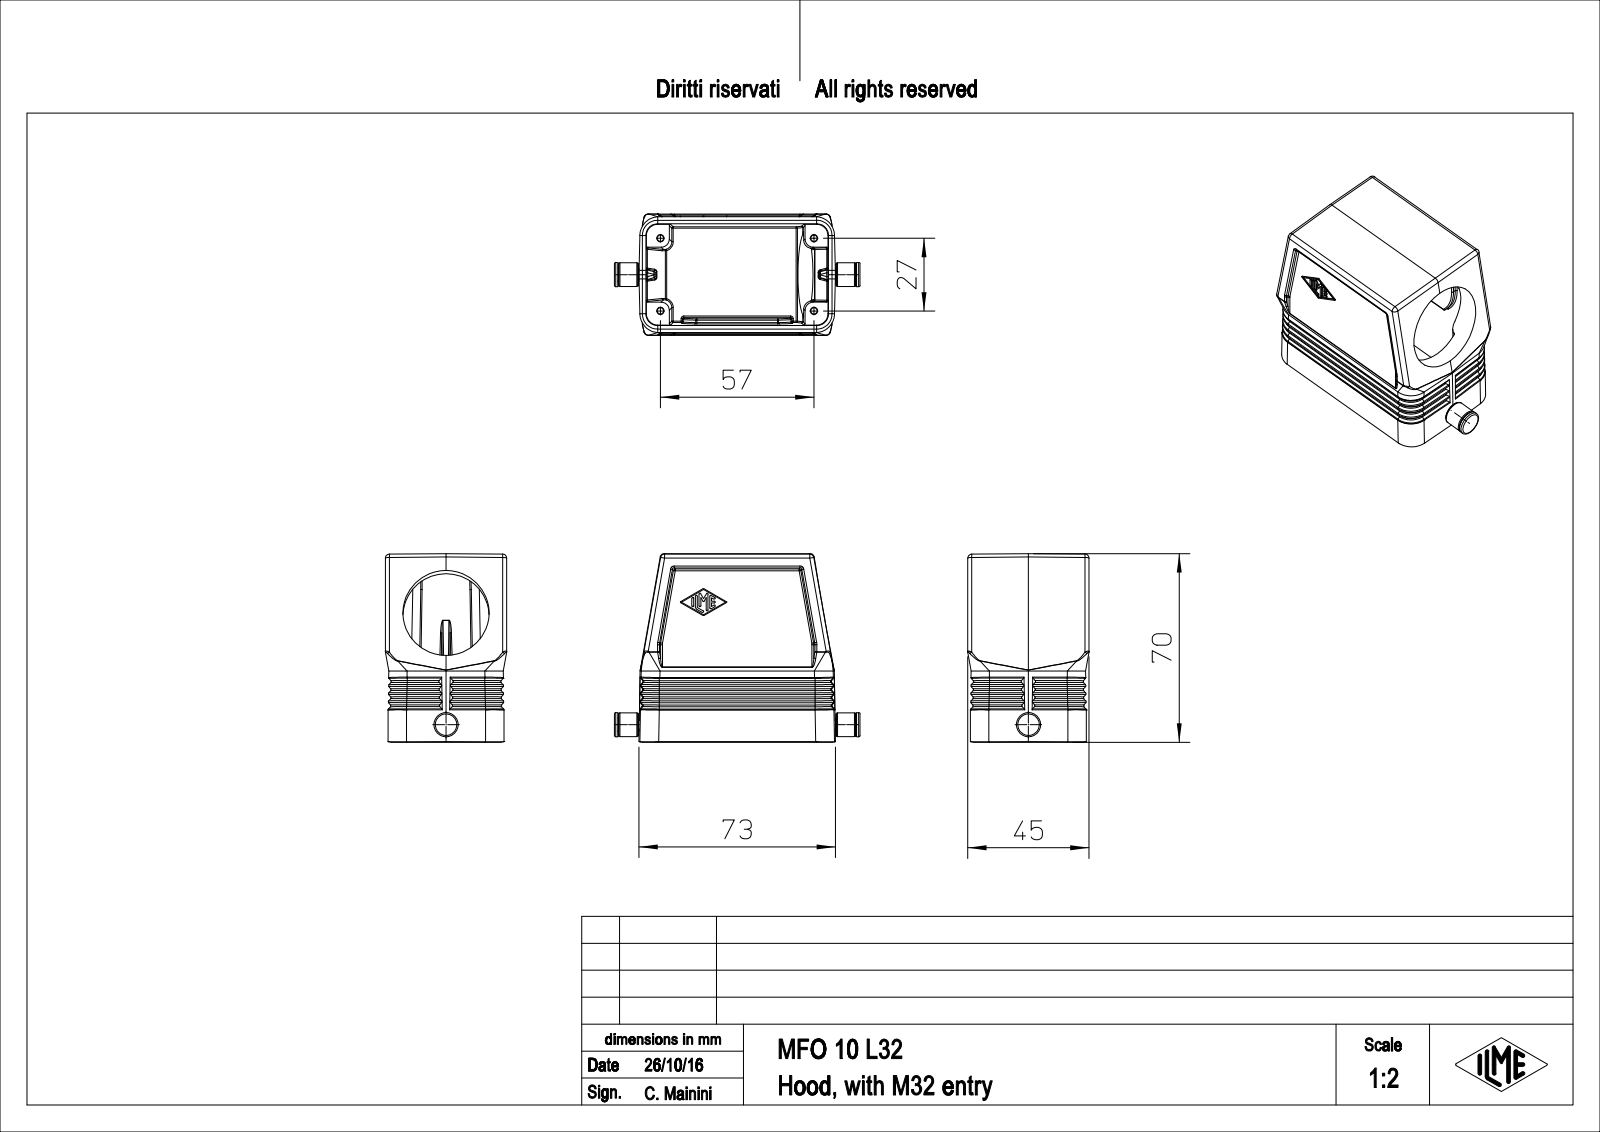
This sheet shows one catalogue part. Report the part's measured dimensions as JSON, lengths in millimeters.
{"part_name": "MFO_10_L32", "step_written_by": "PTC Creo Elements/Direct Modeling 19.0E 27-Jun-2016 (C) Parametric Technology GmbH (AUTOMOTIVE_DESIGN)", "units": "millimeters", "bodies": {"solids": 1, "faces": 431, "planar": 149, "cylindrical": 100, "other": 182}, "overall_size": [91.19, 70, 45], "volume_mm3": 65612, "surface_area_mm2": 33429, "round_holes": [[2.75, 4], [32, 1]], "round_bosses_or_shafts": [[9, 1], [8.8, 1], [4.8, 1], [3.2, 1]], "partial_cylinders_radius": [[0.5, 16], [1, 14], [1.5, 10], [7, 8], [3, 4], [4.2, 4], [6, 4], [20, 1]], "face_to_face_distances": [43, 8.5, 1.91, 2, 44, 1, 4, 45, 6, 11.35], "hole_center_spacings": [27, 57, 63.07]}
